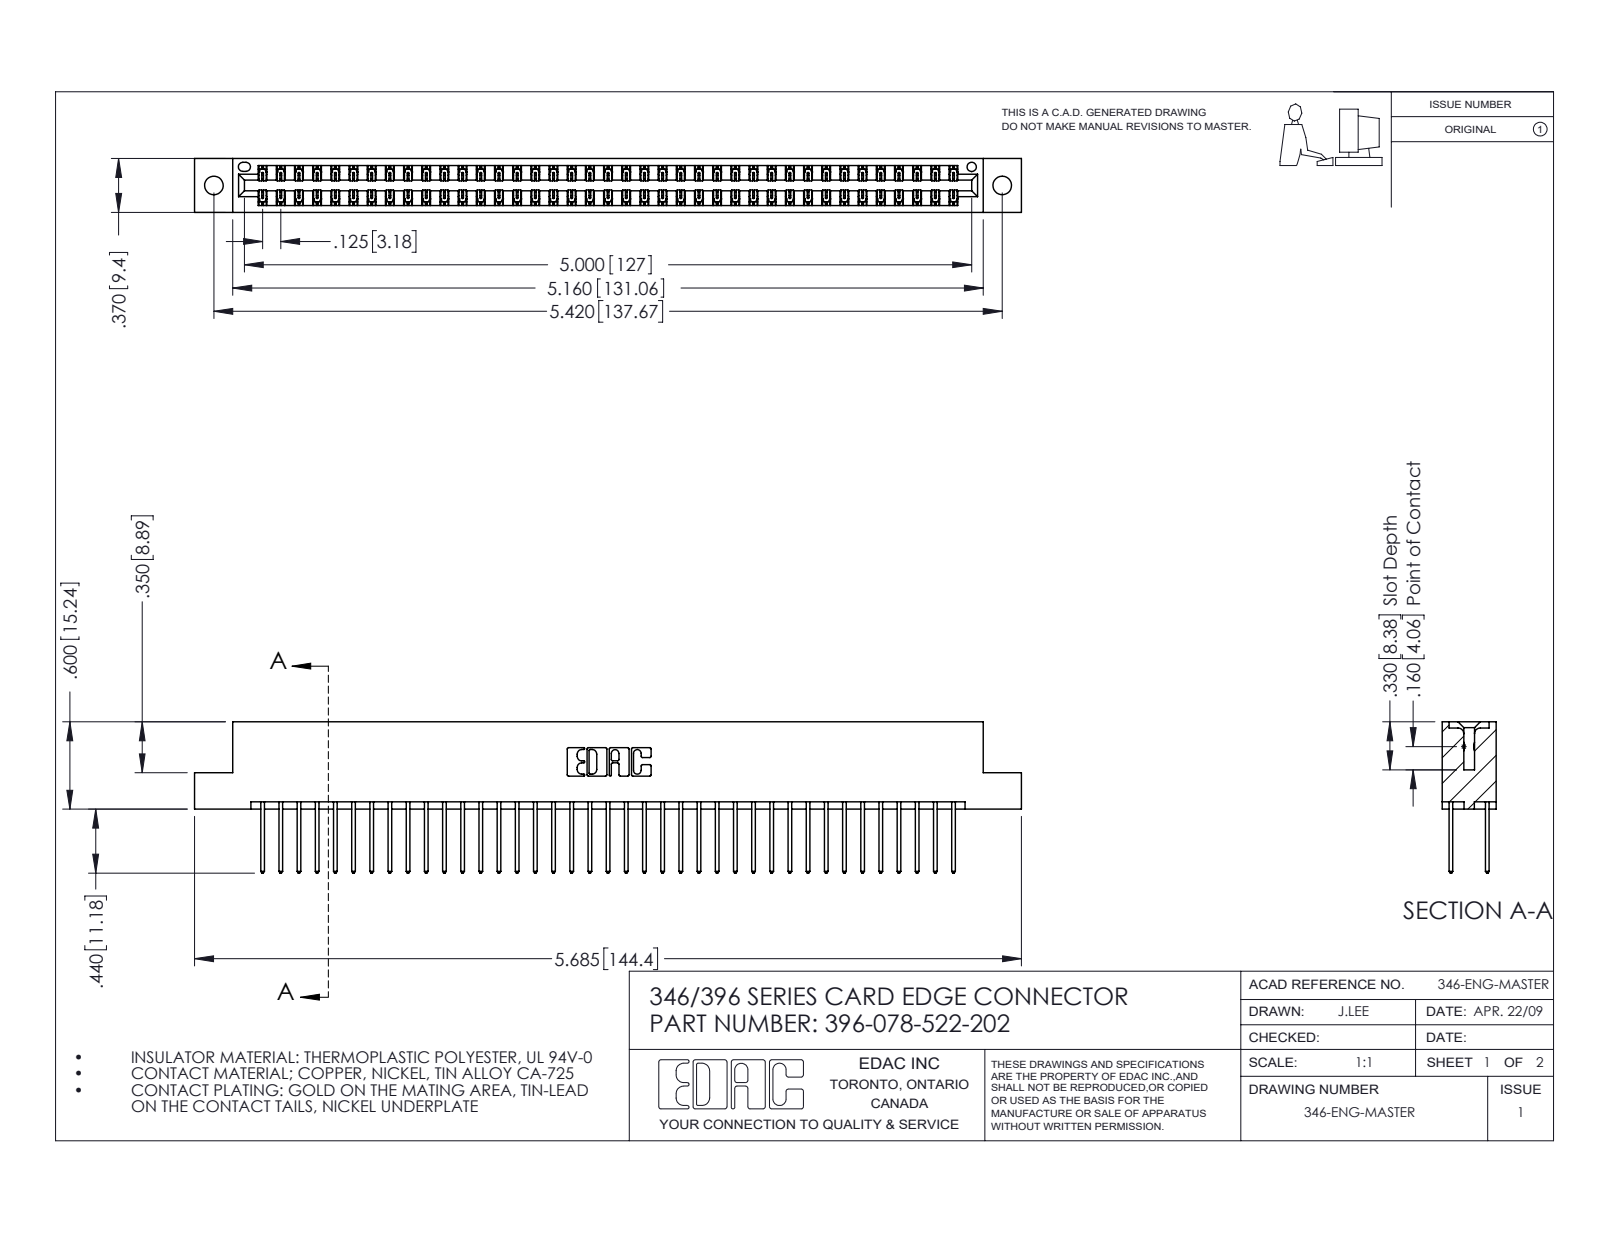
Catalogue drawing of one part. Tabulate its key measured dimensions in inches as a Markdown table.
| quantity | value |
| --- | --- |
| part name | 396-078-522-202; 346 Part_Flush Mounting Lugs - 0.128 Dia; 345-292-001_345-293-122 |
| STEP written by | SolidWorks 2016 (CONFIG_CONTROL_DESIGN) |
| units | inches |
| bodies | 79 solids, 4178 faces (2806 planar, 1372 cylindrical, 0 other) |
| overall size | 5.685 × 1.04 × 0.37 |
| volume | 0.868 in³ |
| surface area | 31.24 in² |
| round holes (diameter × count) | 0.128 × 2, 0.064 × 1 |
| partial cylindrical surfaces (radius × count) | 0.006 × 117, 0.01 × 78, 0.01 × 22, 0.007 × 6, 0.031 × 6, 0.026 × 3, 0.014 × 2, 0.022 × 2 |
| main face-to-face distances | 0.048, 0.322, 0.25, 0.37, 0.072, 0.298, 0.025, 0.275, 0.148, 0.222 |
| hole center spacings | 0.246, 5.211, 5.42 |
